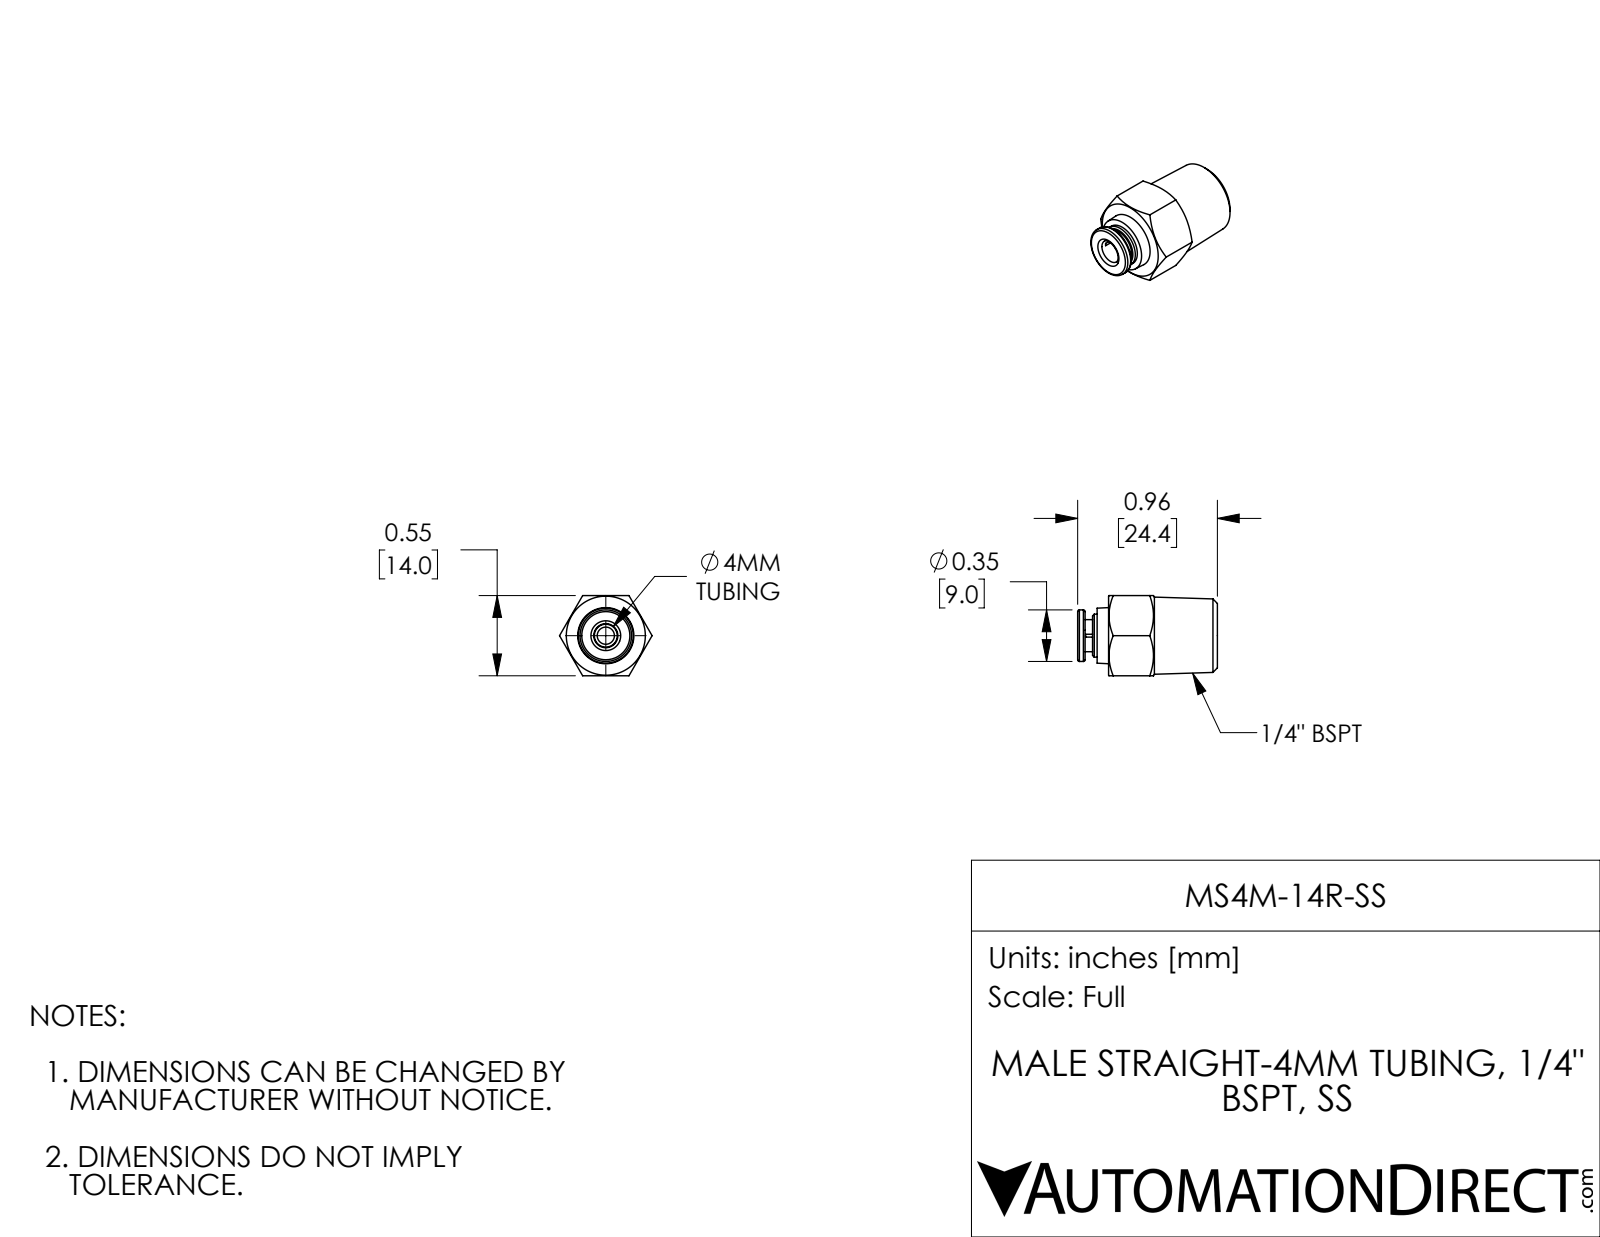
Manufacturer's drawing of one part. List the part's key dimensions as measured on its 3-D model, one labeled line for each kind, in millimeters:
Part name (STEP PRODUCT): MS4M-14R-SS
STEP written by: SolidWorks 2017 (AUTOMOTIVE_DESIGN)
Units: millimetres
Bodies: 1 solid, 54 faces (20 planar, 10 cylindrical, 24 other)
Overall size (bounding box): 24.4 × 16.2 × 14
Volume: 2 830 mm³ · Surface area: 1 623 mm²
Round holes (diameter × count): ⌀3 ×1, ⌀4.2 ×1
Round bosses / shafts (diameter × count): ⌀9 ×1, ⌀7.5 ×1, ⌀5.6 ×1
Main face-to-face distances: 14, 19, 1.3, 24.4, 5.4, 23.1, 4.1, 2, 21, 2.1
